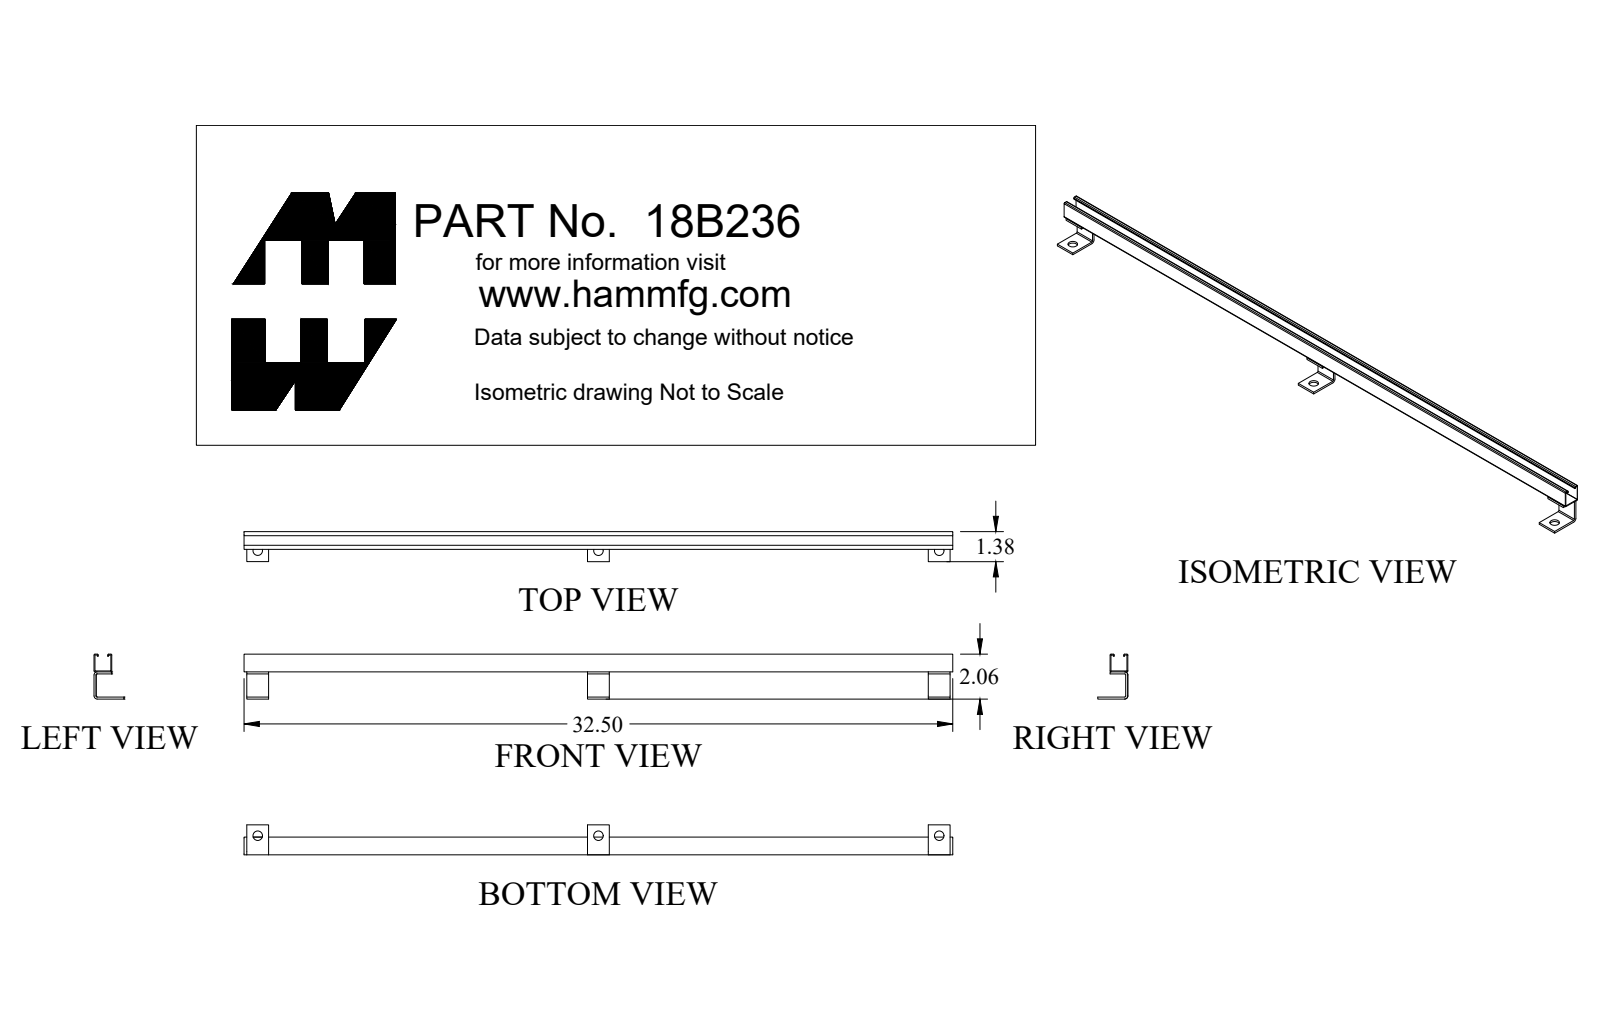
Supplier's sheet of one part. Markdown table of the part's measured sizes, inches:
| quantity | value |
| --- | --- |
| part name | 18B236 |
| STEP written by | SolidWorks 2018 (AUTOMOTIVE_DESIGN) |
| units | inches |
| bodies | 4 solids, 75 faces (48 planar, 27 cylindrical, 0 other) |
| overall size | 32.5 × 2.063 × 1.376 |
| volume | 4.374 in³ |
| surface area | 199.4 in² |
| round holes (diameter × count) | 0.437 × 3 |
| partial cylindrical surfaces (radius × count) | 0.043 × 6, 0.048 × 4, 0.143 × 4 |
| main face-to-face distances | 0.04, 0.773, 0.813, 0.733, 0.773, 0.095, 0.813, 0.733, 0.148, 0.625 |
| hole center spacings | 15.625, 31.25 |
